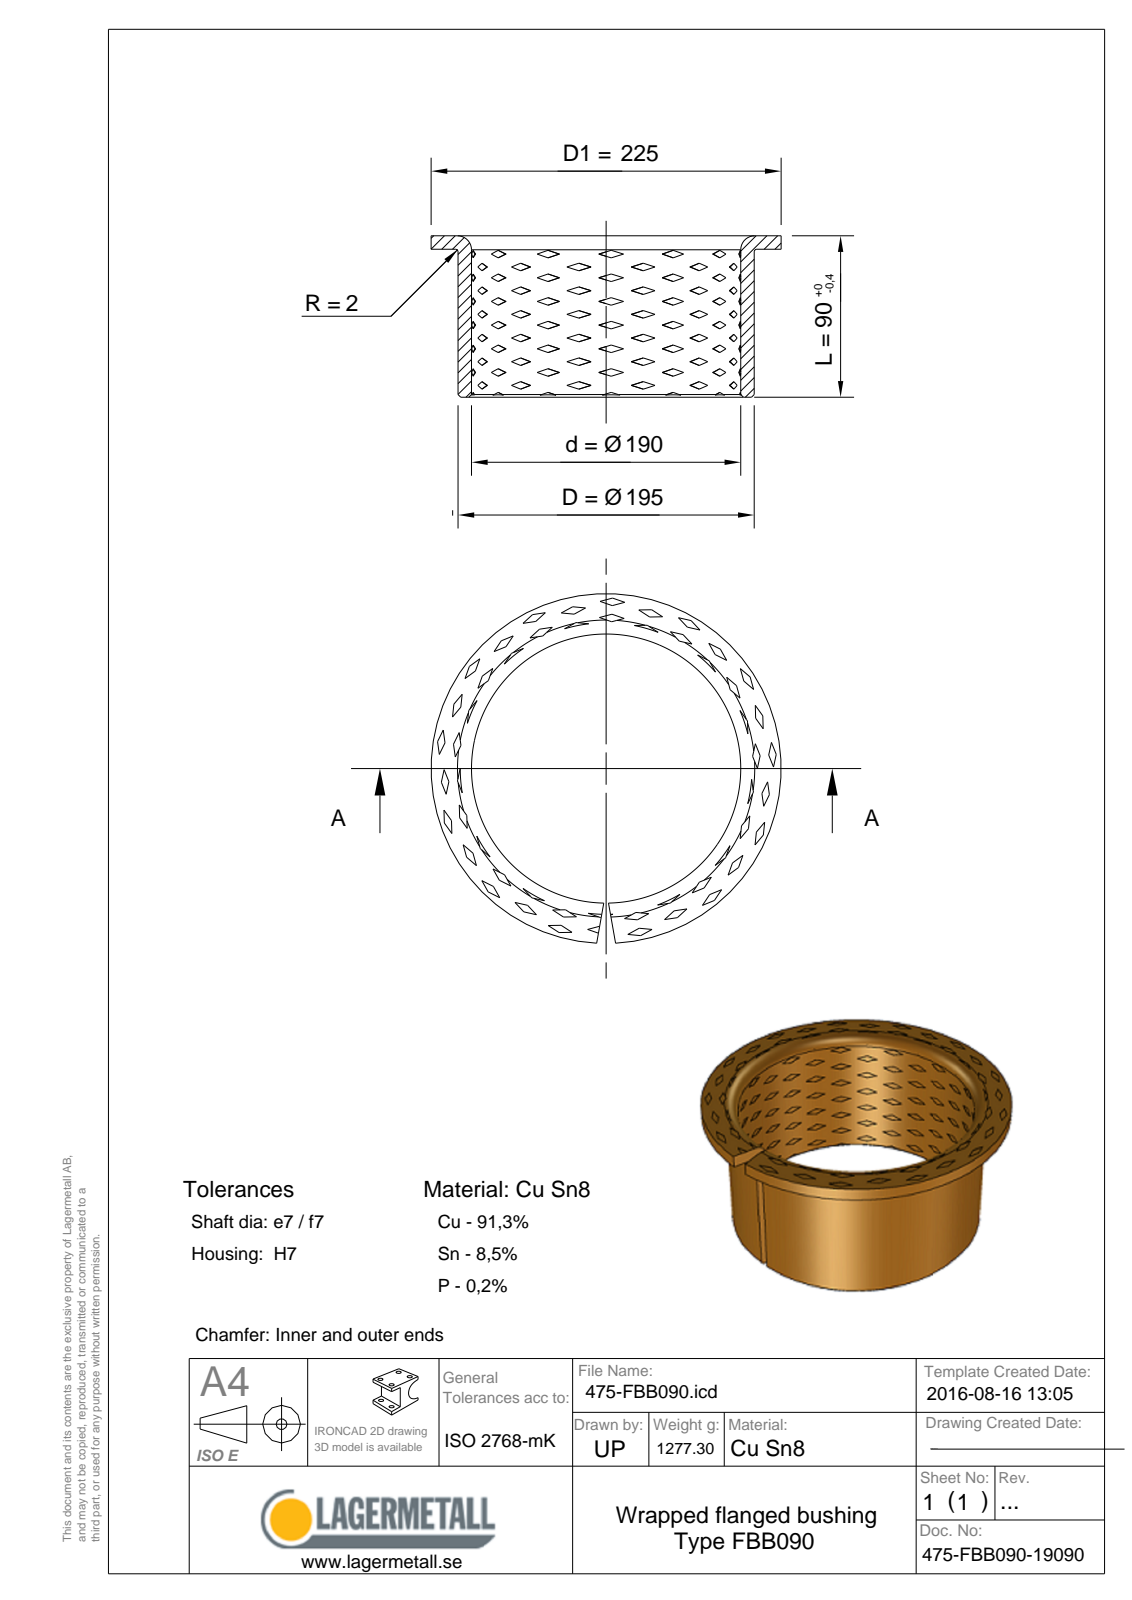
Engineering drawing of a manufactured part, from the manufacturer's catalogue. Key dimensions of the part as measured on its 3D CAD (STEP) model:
Part name (STEP PRODUCT): 475-FBB090-19090
STEP written by: Spatial InterOp 3D (CONFIG_CONTROL_DESIGN)
Units: millimetres
Bodies: 1 solid, 12 faces (5 planar, 3 cylindrical, 4 other)
Overall size (bounding box): 225 × 224.94 × 90
Volume: 157 691 mm³ · Surface area: 129 765 mm²
Round holes (diameter × count): ⌀190 ×1
Round bosses / shafts (diameter × count): ⌀225 ×1, ⌀195 ×1
Main face-to-face distances: 2.5, 87.5, 90
